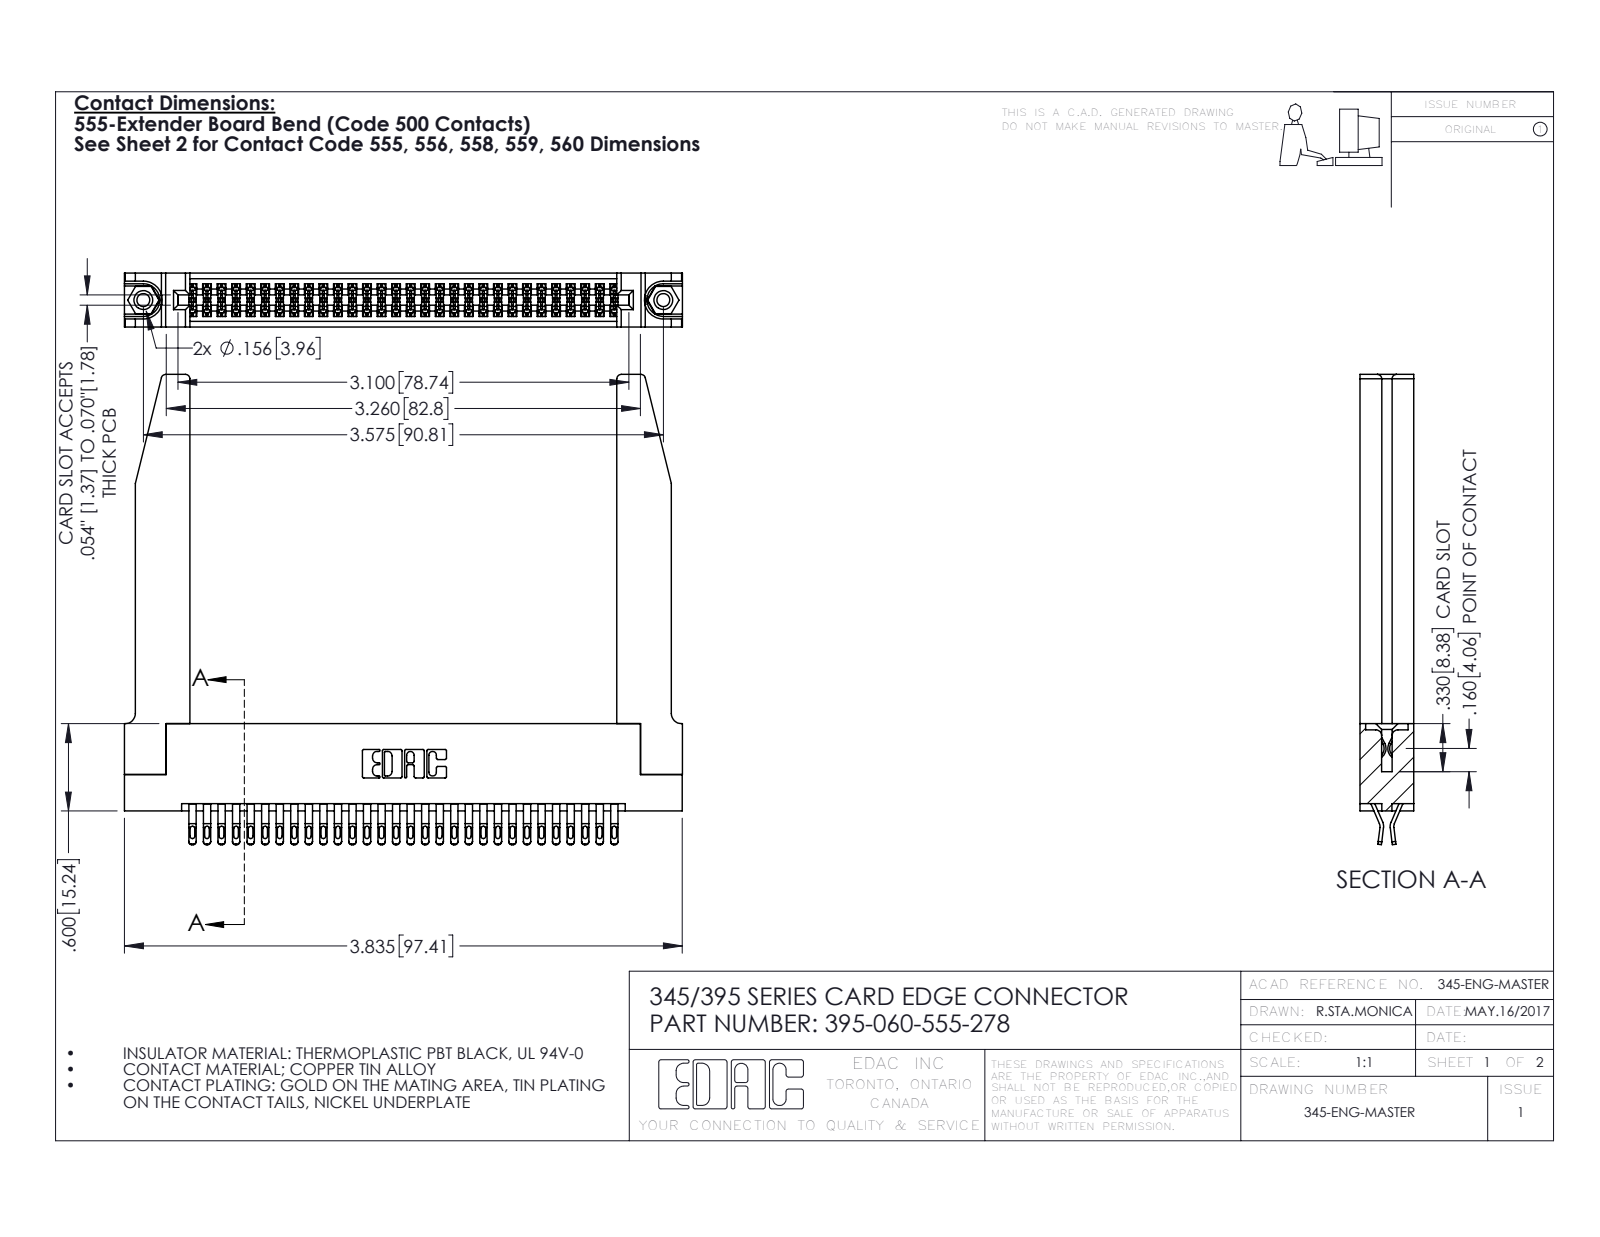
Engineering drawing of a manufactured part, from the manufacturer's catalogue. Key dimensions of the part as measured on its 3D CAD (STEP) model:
Part name (STEP PRODUCT): 345-250-001_345-250-001-102; 345-220-078_345-220-078; 395-060-555-278; 345 Part_Flush Mounting Lugs - 0.156 Dia-TH (+1 more)
STEP written by: SolidWorks 2016 (CONFIG_CONTROL_DESIGN)
Units: inches
Bodies: 65 solids, 3720 faces (2082 planar, 1586 cylindrical, 52 other)
Overall size (bounding box): 3.836 × 3.232 × 0.37
Volume: 1.056 in³ · Surface area: 33.01 in²
Round holes (diameter × count): ⌀0.089 ×2, ⌀0.125 ×2, ⌀0.156 ×2, ⌀0.064 ×1
Round bosses / shafts (diameter × count): ⌀0.155 ×2
Partial cylindrical surfaces — rounded edges, fillets, slot ends (radius × count): R0.016 ×150, R0.02 ×120, R0.006 ×90, R0.01 ×22, R0.03 ×8, R0.007 ×6, R0.031 ×6, R0.026 ×3
Main face-to-face distances: 0.37, 0.072, 0.298, 0.2, 0.025, 0.098, 0.272, 0.225, 0.148, 0.15
Hole centre spacings: 0.27, 3.34, 3.575
